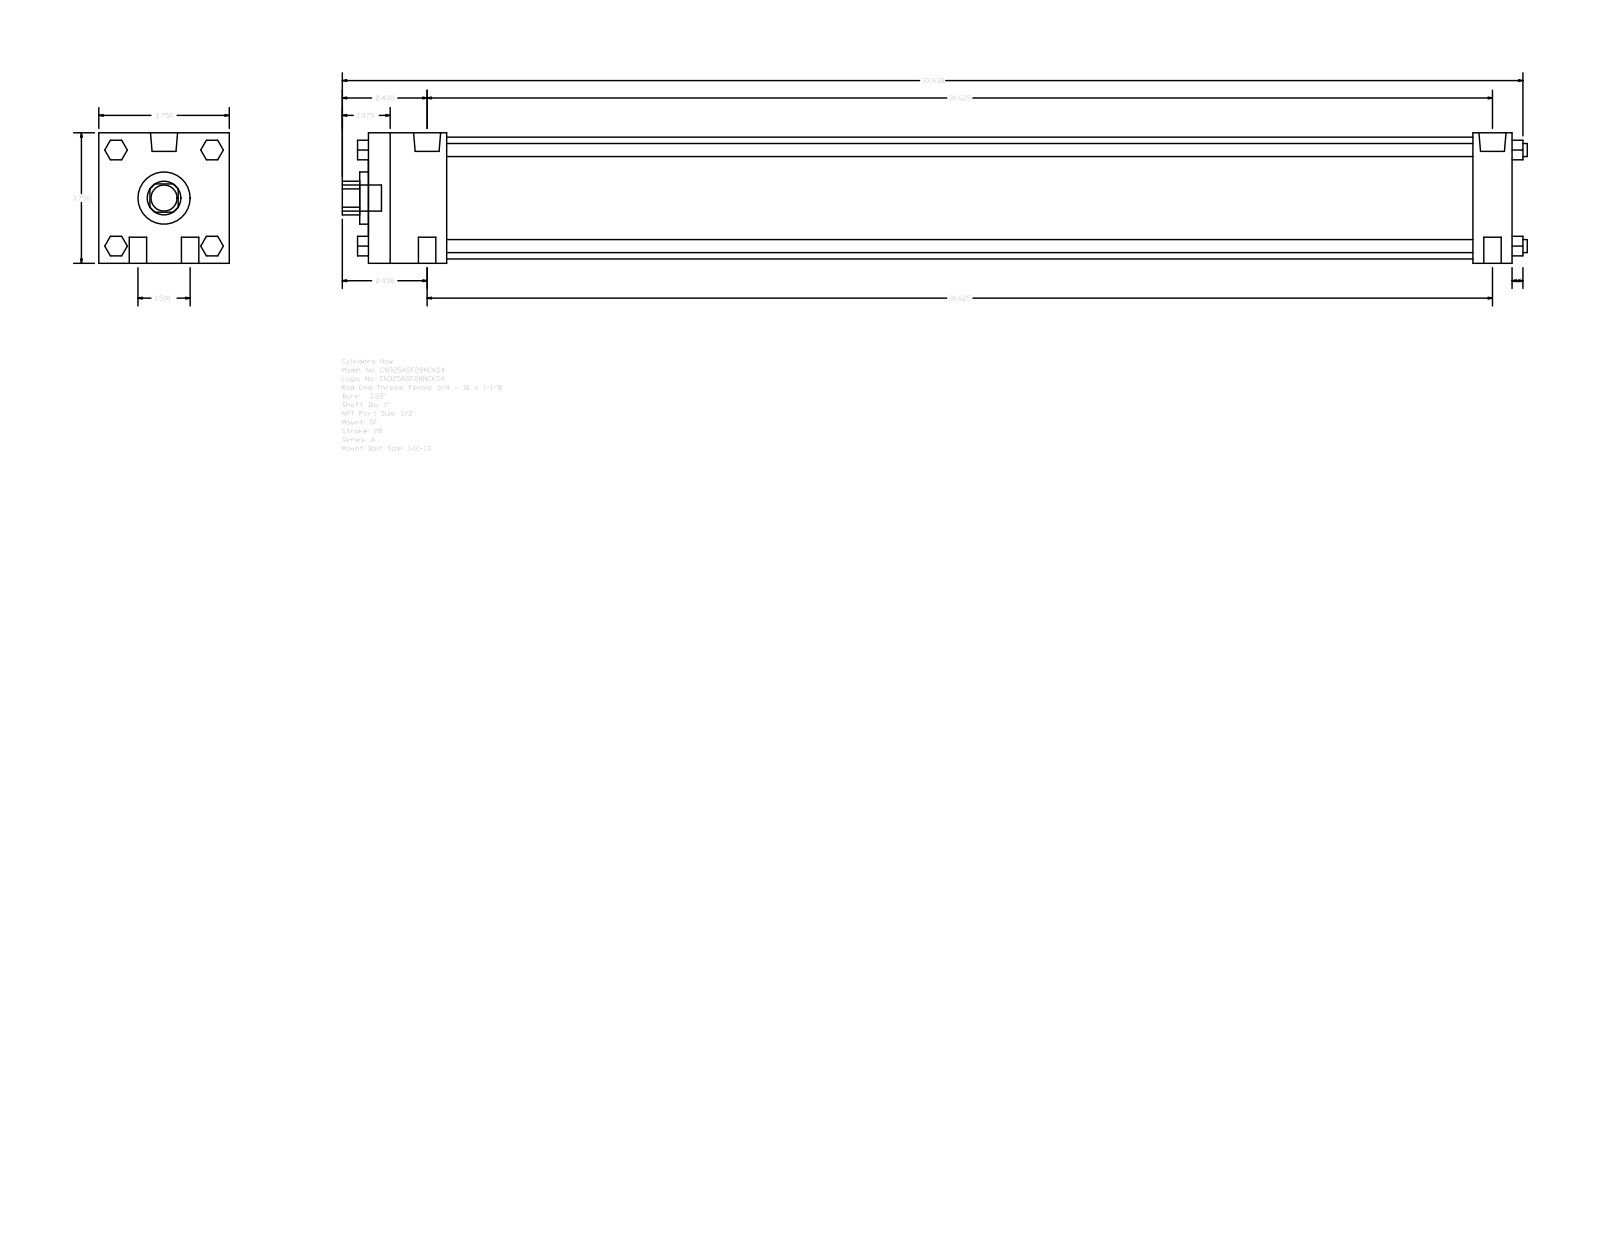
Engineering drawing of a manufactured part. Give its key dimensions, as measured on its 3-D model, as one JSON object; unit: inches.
{"part_name": "A_SF__0325_1", "step_written_by": "GSSL Pune (CONFIG_CONTROL_DESIGN)", "units": "inches", "bodies": {"solids": 0, "faces": 124, "planar": 94, "cylindrical": 30, "other": 0}, "overall_size": [34.063, 3.75, 3.75], "round_holes": [[1, 1], [1.5, 1], [3.5, 1]], "round_bosses_or_shafts": [[0.5, 4], [0.375, 4], [0.778, 2], [0.344, 2], [0.75, 1]], "partial_cylinders_radius": [[0.484, 1]], "face_to_face_distances": [3.75, 32.875, 31.75, 1.125, 2.25, 29.5, 30.625, 0.562, 1.38, 2.39]}
